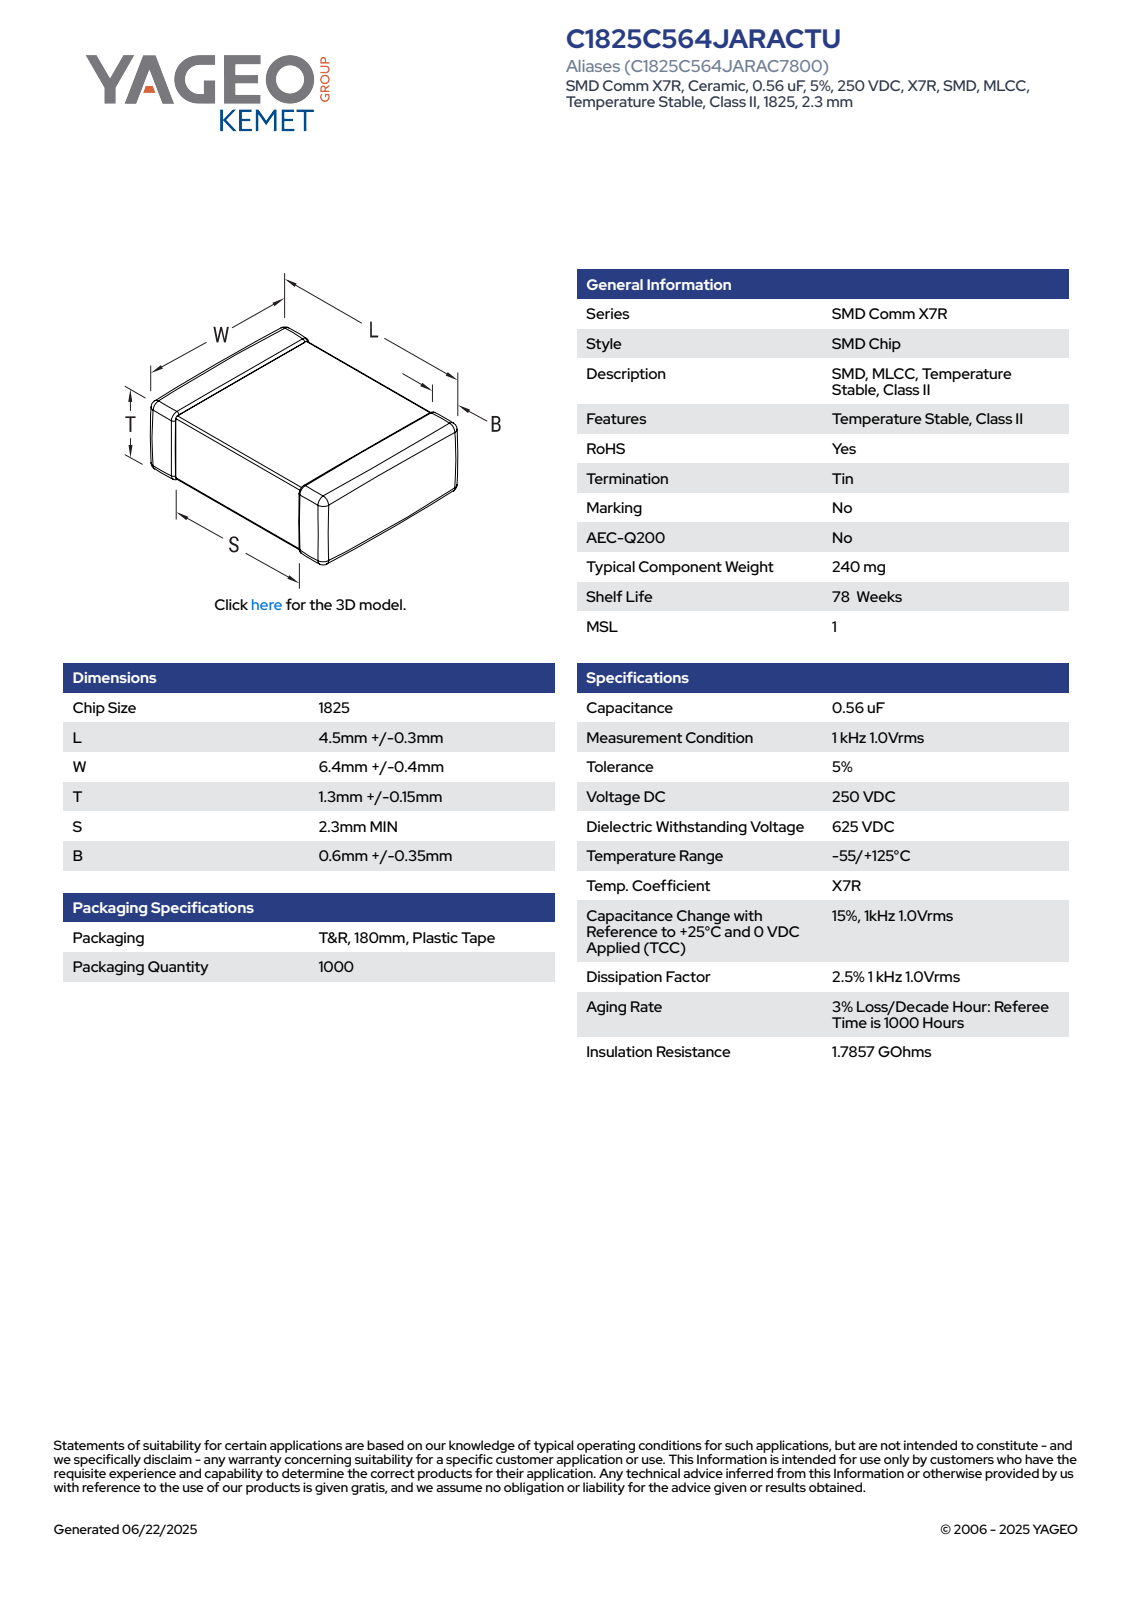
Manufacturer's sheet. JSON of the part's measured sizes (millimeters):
{"part_name": "CCS_CCSTD_1825_L4.8W6.8T1.45B0.6", "step_written_by": "SolidWorks 2021 (AUTOMOTIVE_DESIGN)", "units": "millimeters", "bodies": {"solids": 4, "faces": 125, "planar": 71, "cylindrical": 38, "other": 16}, "overall_size": [6.8, 4.8, 1.45], "volume_mm3": 40, "surface_area_mm2": 101, "partial_cylinders_radius": [[0.14, 24]], "face_to_face_distances": [1.17, 1.31, 1.45, 4.8, 6.66, 6.52, 6.8, 1.59, 3.21, 2.59]}
